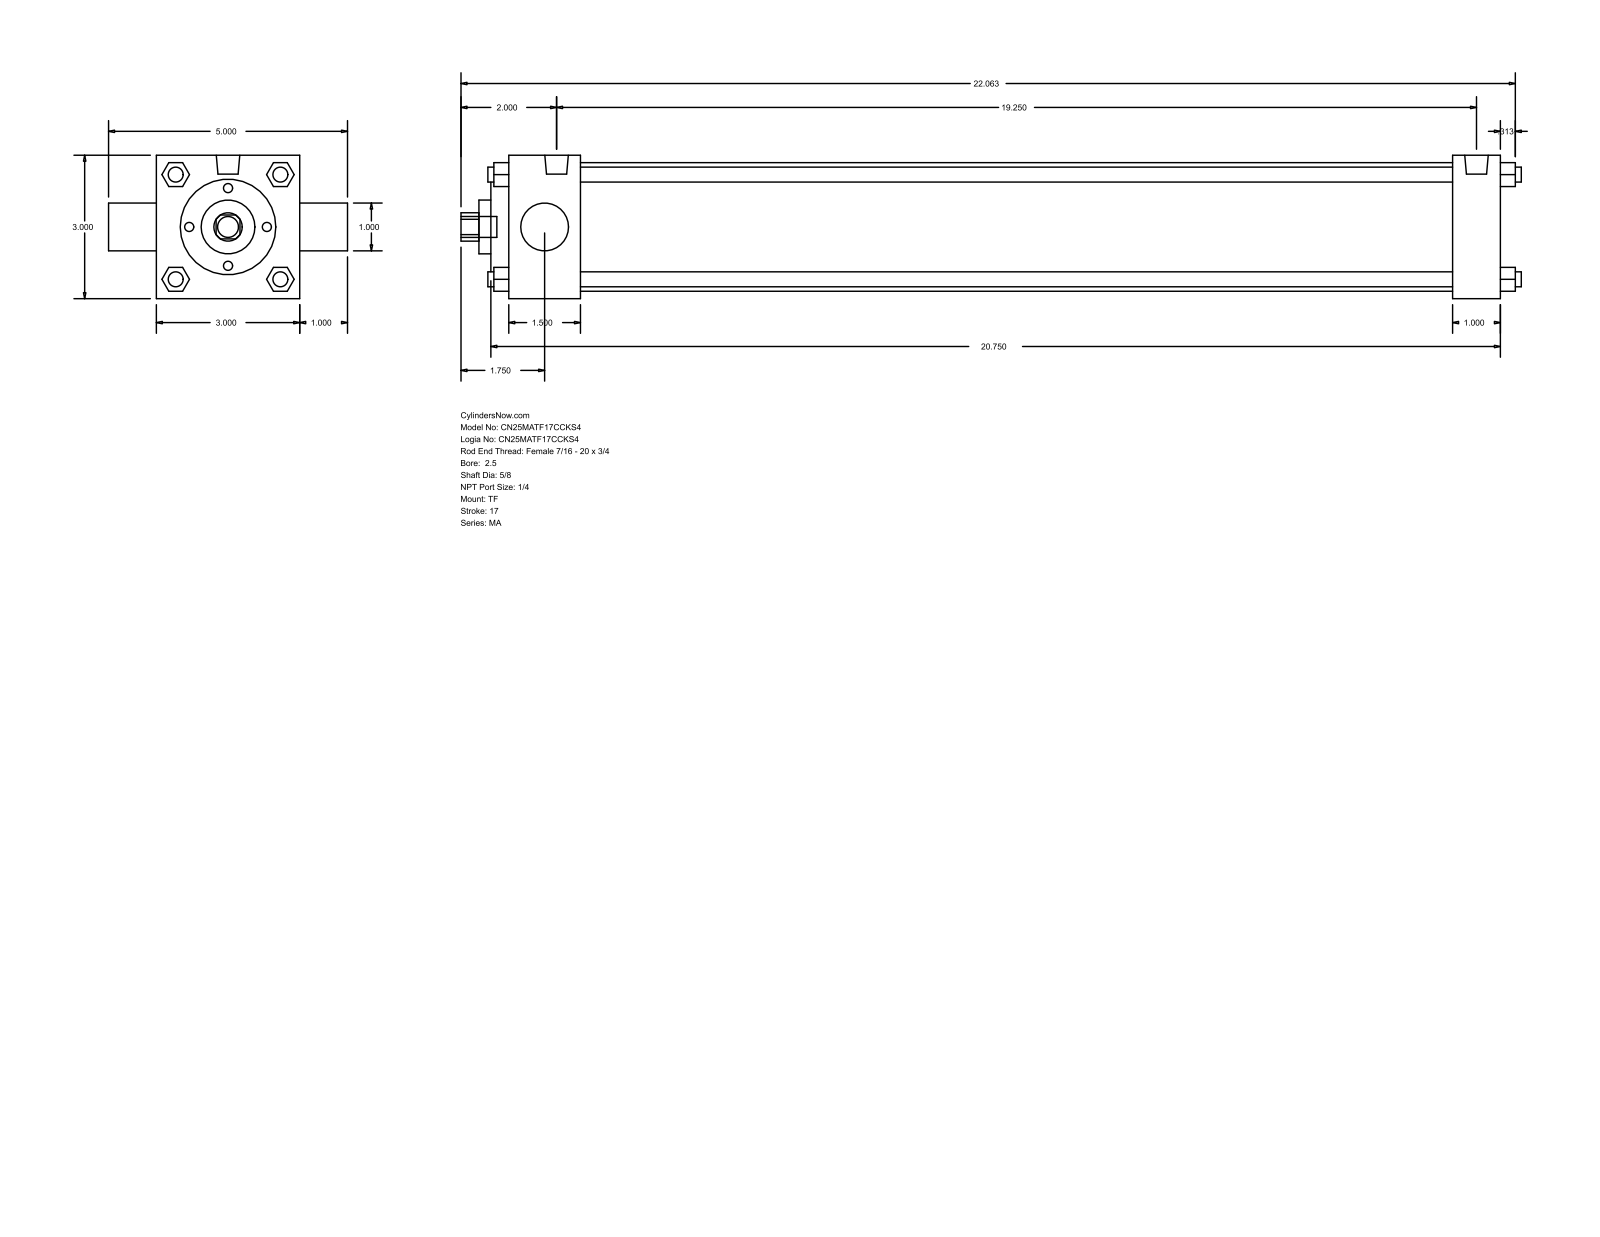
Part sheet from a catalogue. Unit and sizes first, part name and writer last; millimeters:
Units: millimetres
Overall size (bounding box): 563.56 × 127 × 76.2
Round holes (diameter × count): ⌀15.88 ×1, ⌀25.4 ×1, ⌀28.57 ×1, ⌀50.8 ×1, ⌀68.33 ×1
Round bosses / shafts (diameter × count): ⌀7.94 ×7, ⌀12.49 ×2, ⌀11.11 ×1
Partial cylindrical surfaces — rounded edges, fillets, slot ends (radius × count): R7.54 ×1
Main face-to-face distances: 76.2, 527.05, 25.4, 38.1, 501.65, 463.55, 488.95, 12.7, 9.52, 47.62
Bodies: 0 solids, 122 faces (93 planar, 29 cylindrical, 0 other)
Part name (STEP PRODUCT): MA_TF__0250_0.625
STEP written by: GSSL Pune (CONFIG_CONTROL_DESIGN)
